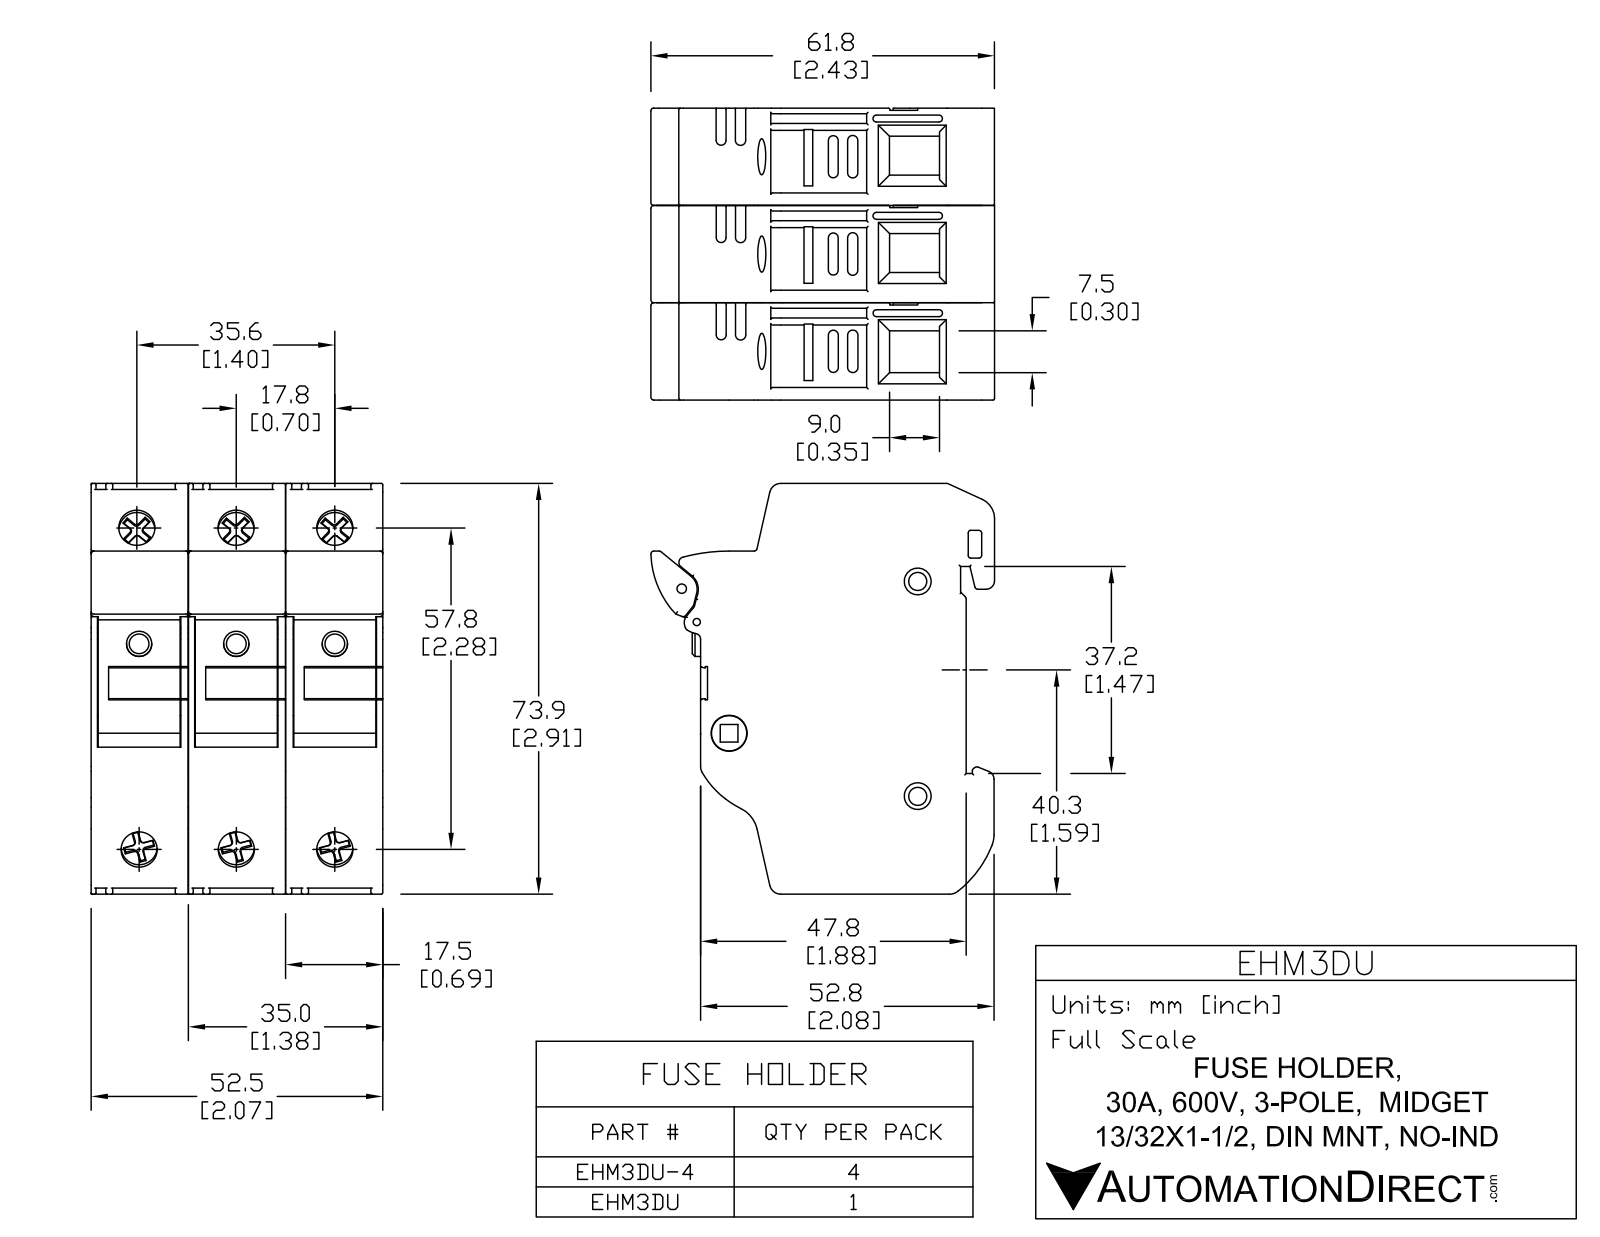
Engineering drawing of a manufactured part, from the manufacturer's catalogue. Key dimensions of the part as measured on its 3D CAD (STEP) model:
Part name (STEP PRODUCT): EHM3DU
STEP written by: SolidWorks 2011 (AUTOMOTIVE_DESIGN)
Units: millimetres
Bodies: 1 solid, 1684 faces (756 planar, 570 cylindrical, 358 other)
Overall size (bounding box): 73.88 × 61.82 × 52.52
Volume: 158 176 mm³ · Surface area: 48 319 mm²
Round holes (diameter × count): ⌀6.5 ×6, ⌀3.25 ×2, ⌀4.83 ×2, ⌀1.3 ×1, ⌀1.7 ×1, ⌀6.48 ×1
Round bosses / shafts (diameter × count): ⌀6.35 ×1
Partial cylindrical surfaces — rounded edges, fillets, slot ends (radius × count): R0.25 ×94, R0.2 ×80, R0.62 ×12, R0.5 ×11, R2 ×10, R0.51 ×9, R0.89 ×9, R0.92 ×9
Main face-to-face distances: 17.5, 35, 52.5, 1.25, 1.58, 16.25, 27.51, 29.09, 22.94, 24.71
Hole centre spacings: 17.51, 35.02, 6.58, 20.83, 27.36, 35.77, 35.79, 38.61
